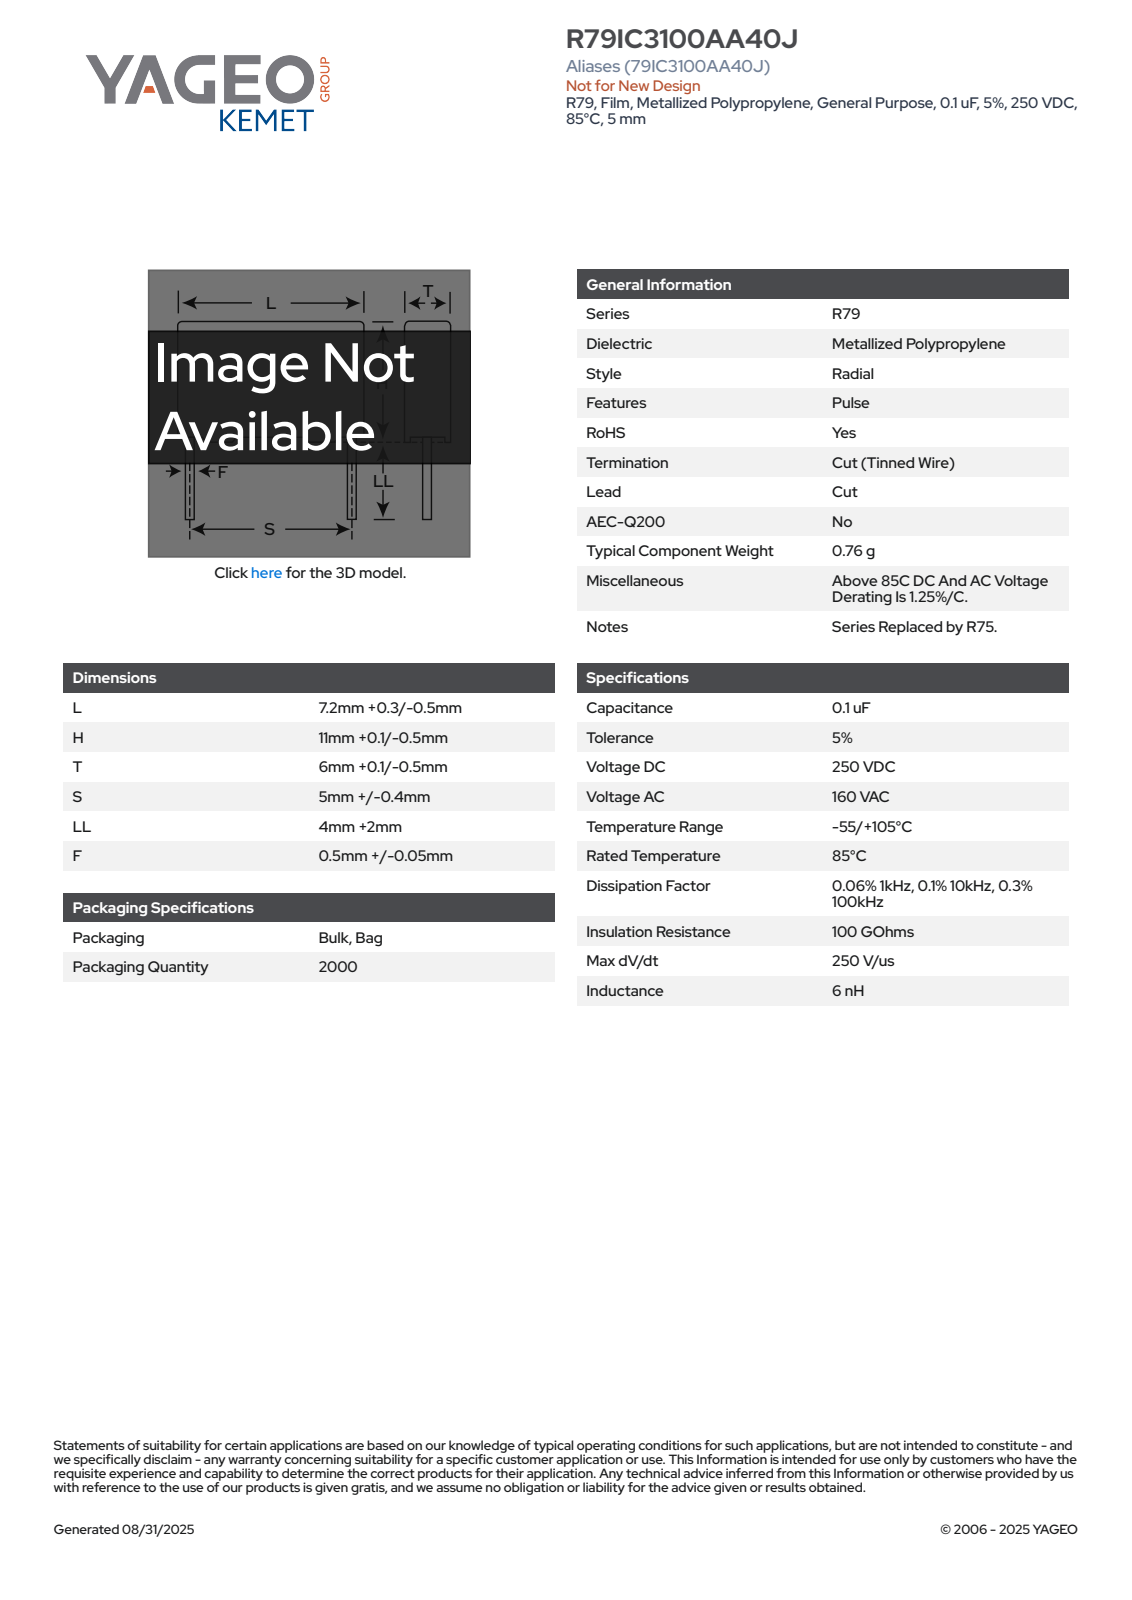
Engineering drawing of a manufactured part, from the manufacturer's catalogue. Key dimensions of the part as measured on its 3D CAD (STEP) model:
Part name (STEP PRODUCT): CFR_RB2_7.2X11X6_L7.5H11.1T6.1S5LL6F0.55
STEP written by: SolidWorks 2014 (AUTOMOTIVE_DESIGN)
Units: millimetres
Bodies: 4 solids, 85 faces (77 planar, 8 cylindrical, 0 other)
Overall size (bounding box): 17.1 × 7.5 × 6.11
Volume: 480 mm³ · Surface area: 431 mm²
Round bosses / shafts (diameter × count): ⌀0.55 ×2
Partial cylindrical surfaces — rounded edges, fillets, slot ends (radius × count): R0.5 ×4
Main face-to-face distances: 6.1, 7.5, 10.35, 5.85, 7.25, 0.75, 11.1, 5.6, 7, 0.38
